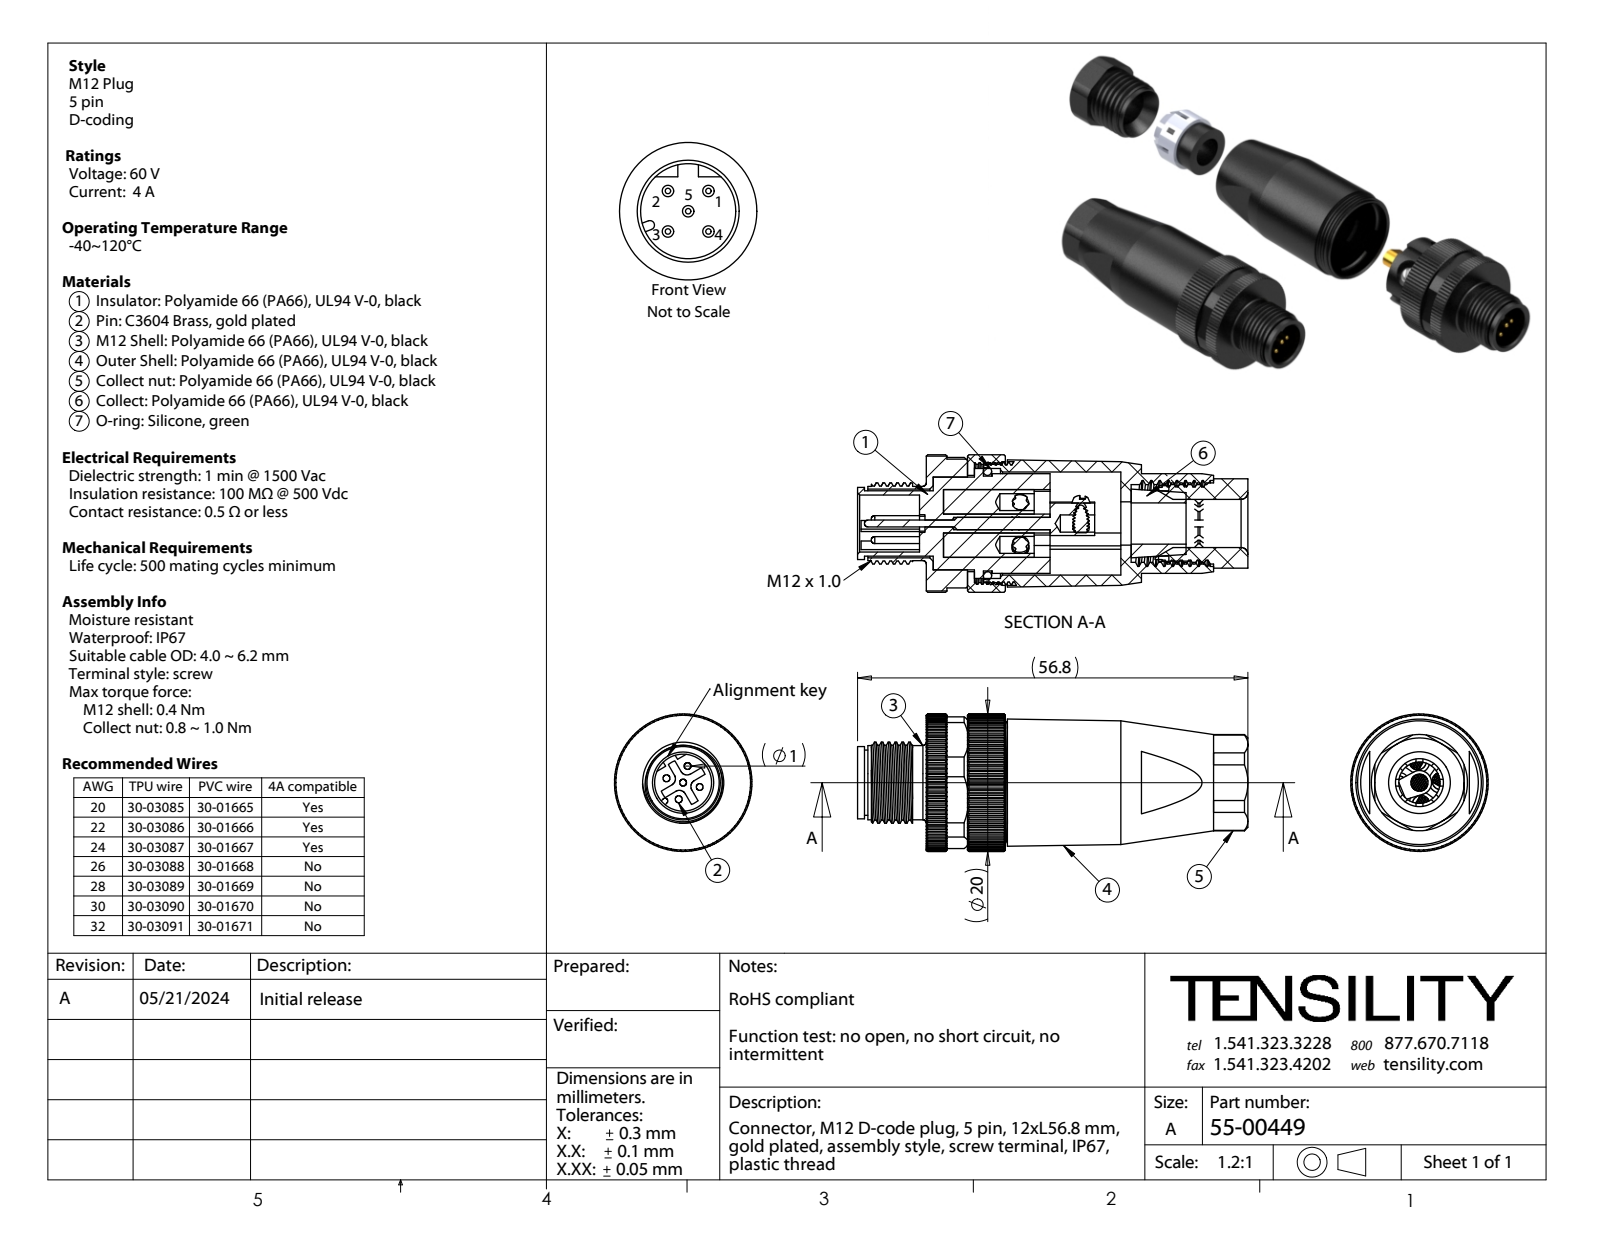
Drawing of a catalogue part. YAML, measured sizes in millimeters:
part_name: "55-00449-05; 55-00449-09; 55-00449-03; 55-00449-11 (+8 more)"
step_written_by: "SolidWorks 2021 (CONFIG_CONTROL_DESIGN)"
units: millimeters
bodies: {solids: 18, faces: 1661, planar: 582, cylindrical: 553, other: 526}
overall_size: [56.8, 20, 20]
volume: 8713
surface_area: 13940
round_holes:
  - {diameter: 2.5, count: 9}
  - {diameter: 1, count: 5}
  - {diameter: 2.05, count: 5}
  - {diameter: 5, count: 4}
  - {diameter: 6, count: 1}
  - {diameter: 6.3, count: 1}
  - {diameter: 7, count: 1}
  - {diameter: 8.3, count: 1}
  - {diameter: 9.5, count: 1}
  - {diameter: 10, count: 1}
  - {diameter: 11.3, count: 1}
  - {diameter: 12.5, count: 1}
round_bosses_or_shafts:
  - {diameter: 3.5, count: 5}
  - {diameter: 2.4, count: 5}
  - {diameter: 20, count: 1}
  - {diameter: 17.8, count: 1}
  - {diameter: 17.03, count: 1}
  - {diameter: 17, count: 1}
  - {diameter: 14.5, count: 1}
  - {diameter: 14, count: 1}
partial_cylinders:
  - {radius: 1.75, count: 5}
  - {radius: 1, count: 4}
  - {radius: 0.4, count: 1}
  - {radius: 3.4, count: 1}
  - {radius: 5.3, count: 1}
  - {radius: 6.45, count: 1}
  - {radius: 6.5, count: 1}
  - {radius: 9.65, count: 1}
face_to_face_distances: [1, 6, 1.5, 27.3, 17, 28.8, 7, 13.86, 12, 5]
hole_center_spacings: [5.14, 5.13, 0.8, 2.5, 3.12, 3.54, 3.62, 4.34]
